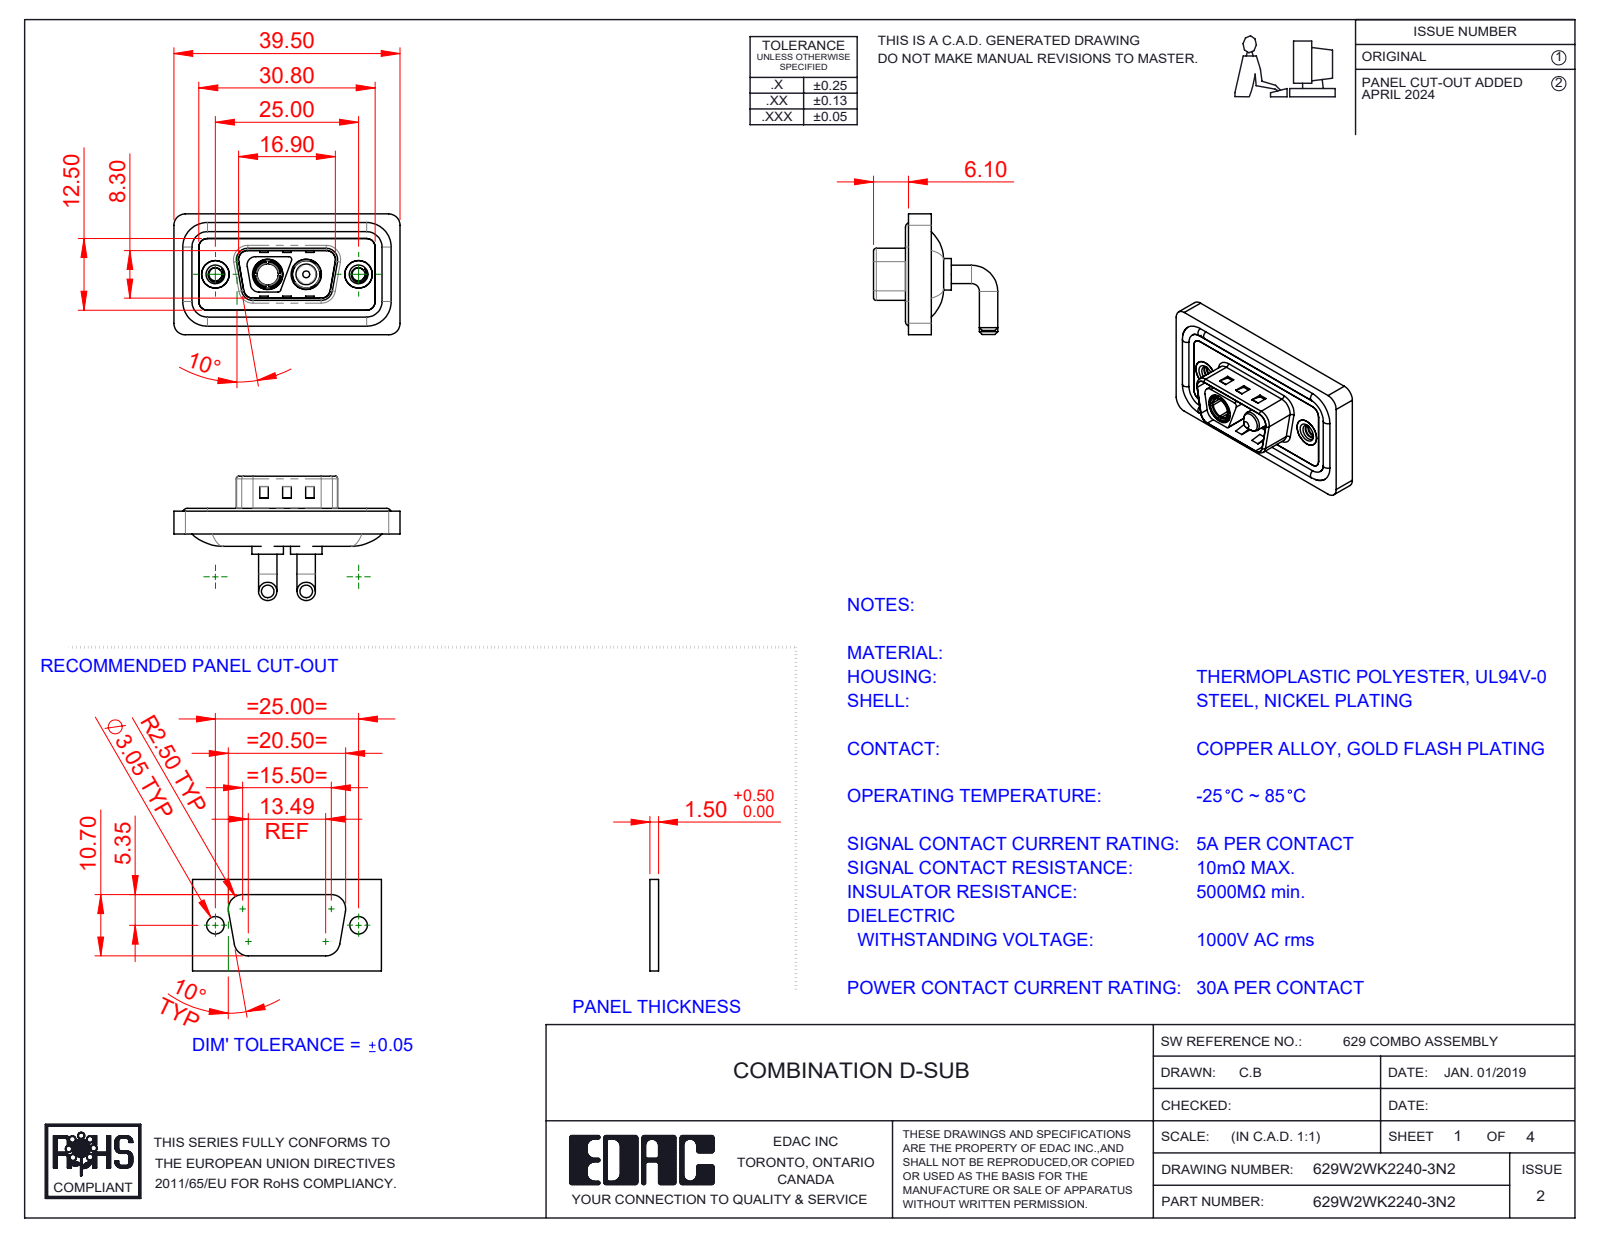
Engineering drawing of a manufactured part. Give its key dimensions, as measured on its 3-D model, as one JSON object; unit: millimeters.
{"part_name": "629Combo Shell Front_09 Contacts; 629Combo Threaded Rivet_2; 629Combo Housing_2WK2; 629Combo Shell Rear_09 Contacts (+4 more)", "step_written_by": "SolidWorks 2023 (CONFIG_CONTROL_DESIGN)", "units": "millimeters", "bodies": {"solids": 11, "faces": 542, "planar": 189, "cylindrical": 231, "other": 122}, "overall_size": [39.5, 21.7, 21.1], "volume_mm3": 4751, "surface_area_mm2": 7570, "round_holes": [[2.26, 2], [4, 2], [4.8, 2], [4.85, 2], [5, 2], [5.3, 2], [3.7, 1]], "round_bosses_or_shafts": [[3.2, 4], [1.6, 4], [5.5, 2], [5.2, 2], [4.9, 2], [4.75, 2], [3.75, 2], [4.96, 1]], "partial_cylinders_radius": [[1.5, 20], [2, 18], [0.5, 10], [1.6, 8], [0.25, 4], [0.6, 4], [0.65, 4], [0.9, 4]], "face_to_face_distances": [0.4, 2.9, 1.1, 0.8, 2.1, 2.5, 3.1, 1.6, 4.5, 1.5], "hole_center_spacings": [9.14, 15.86, 6.72, 25]}
